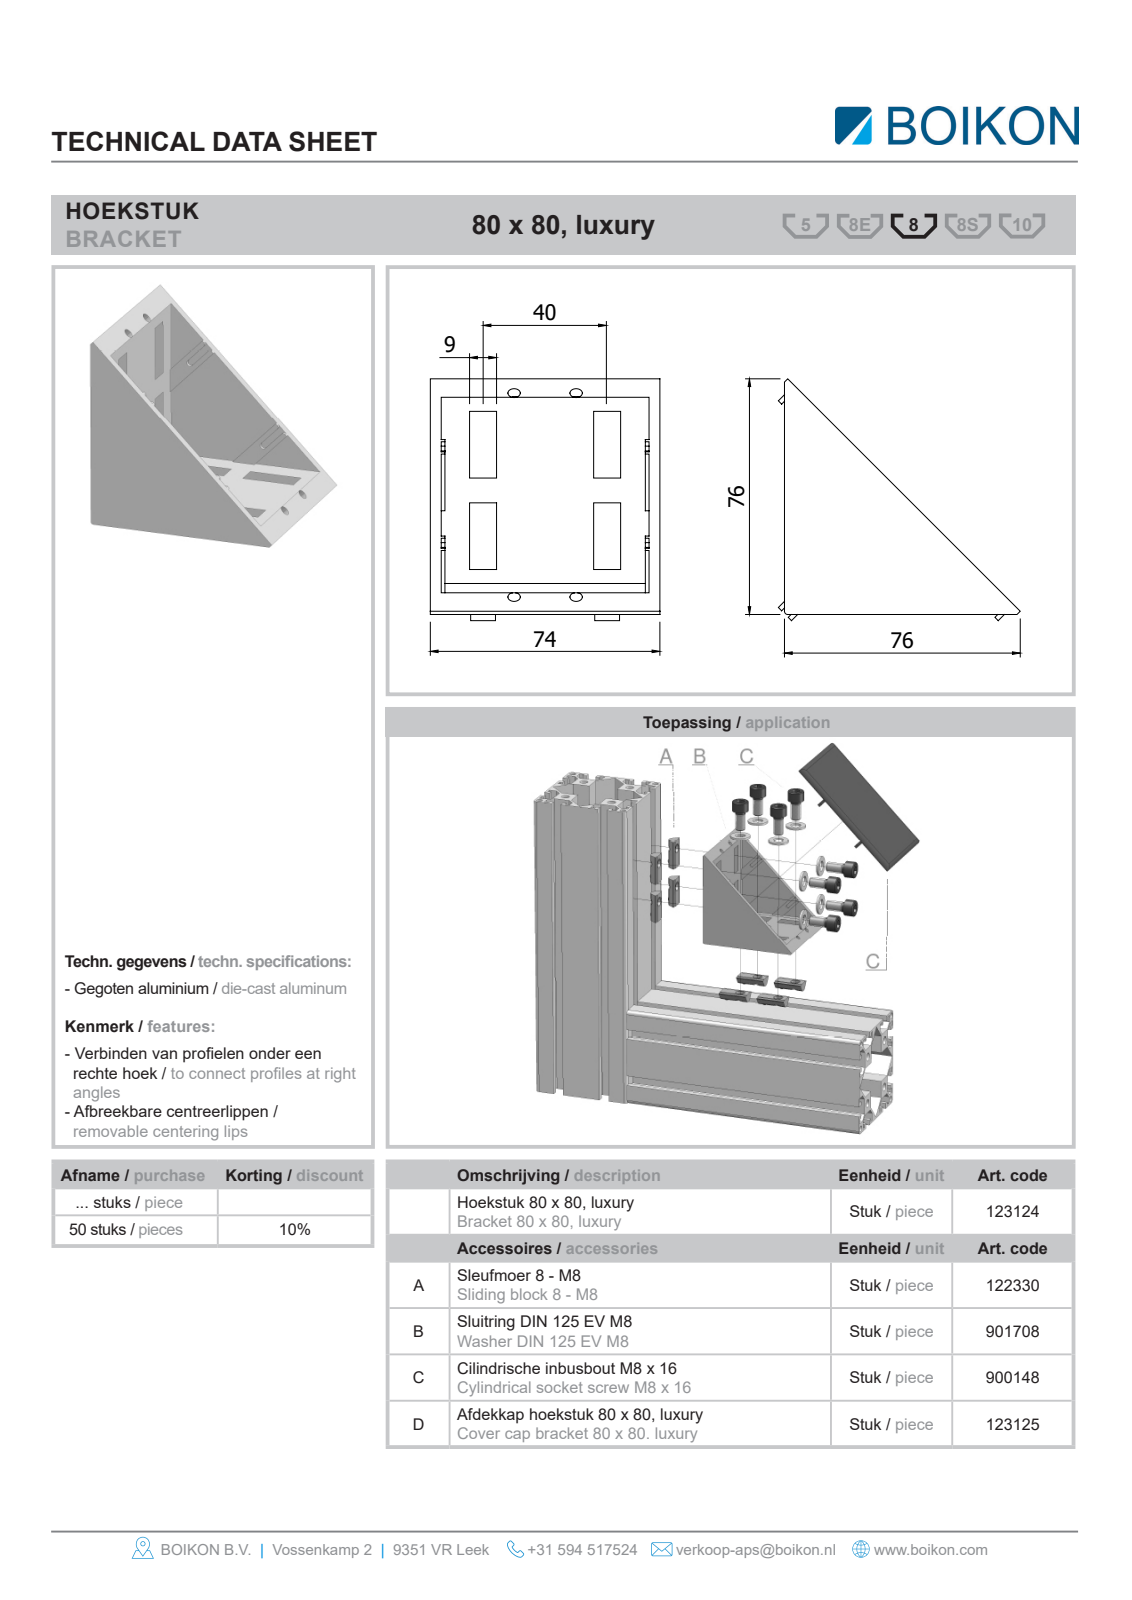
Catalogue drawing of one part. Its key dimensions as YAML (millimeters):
part_name: "Root; 123124HOEKSTUK 80X80 LUXURYBOIKON; 122330Sleufmoer 8 - M8 met kogelBOIKON; 900148Cil. inbusbout DIN 912 EV M8 x 16BOIKON0 (+2 more)"
step_written_by: "HiCAD 2013 1802.4 Build 509 (AUTOMOTIVE_DESIGN)"
units: millimeters
bodies: {solids: 26, faces: 670, planar: 502, cylindrical: 136, other: 32}
overall_size: [89.28, 89.28, 74]
volume: 111457
surface_area: 73740
round_holes:
  - {diameter: 8, count: 8}
  - {diameter: 8.4, count: 8}
  - {diameter: 4, count: 4}
round_bosses_or_shafts:
  - {diameter: 16, count: 8}
  - {diameter: 13, count: 8}
  - {diameter: 6.47, count: 8}
partial_cylinders:
  - {radius: 0.5, count: 8}
  - {radius: 2, count: 8}
  - {radius: 1, count: 5}
  - {radius: 3.5, count: 4}
  - {radius: 5, count: 4}
  - {radius: 1.3, count: 2}
  - {radius: 3, count: 1}
face_to_face_distances: [3, 4, 7, 3.5, 70.5, 74, 1, 0.5, 5.6, 8.6]
hole_center_spacings: [28.5, 40, 49.11, 20, 93, 95.12]
